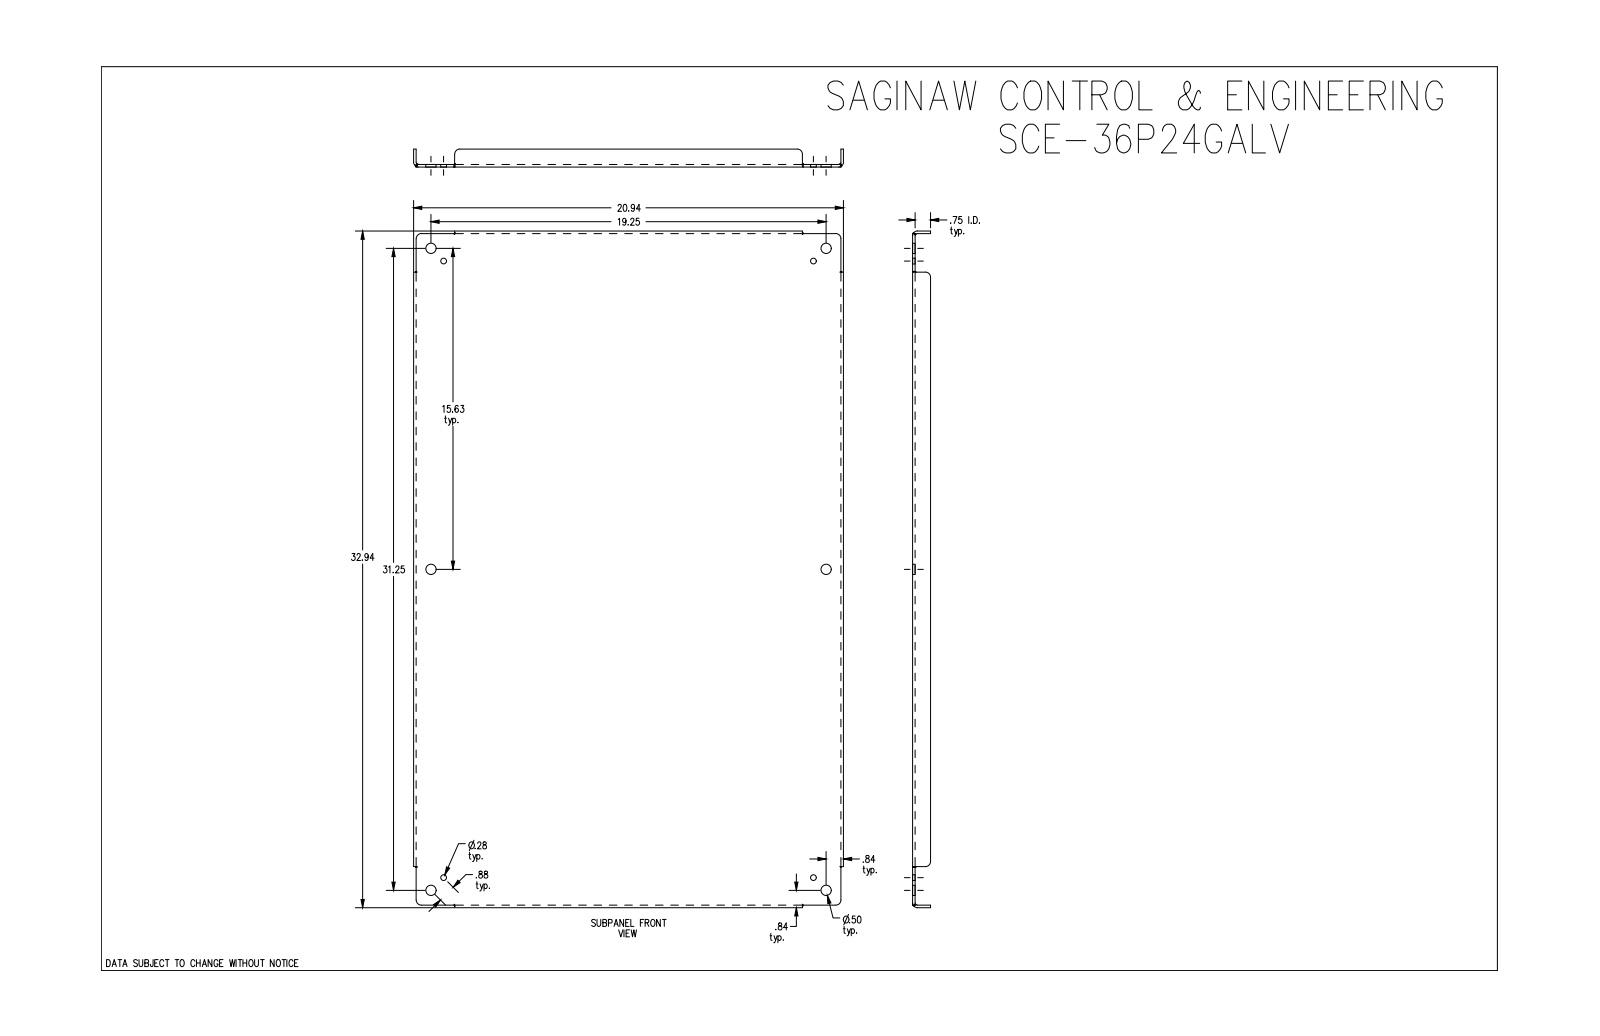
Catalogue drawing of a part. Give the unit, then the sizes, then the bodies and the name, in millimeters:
Units: millimetres
Overall size (bounding box): 836.6 × 531.8 × 22.2
Round holes (diameter × count): ⌀12.7 ×6, ⌀7.1 ×4
Partial cylindrical surfaces — rounded edges, fillets, slot ends (radius × count): R6.4 ×8, R2.8 ×4, R6 ×4
Main face-to-face distances: 3.2, 3.2, 528.7, 833.5, 525.4, 531.8, 19.1, 22.2, 830.2, 836.6
Hole centre spacings: 22.2, 381.5, 396.9, 473.5, 607.6, 629.7, 778.2, 910.7
Volume: 1 532 000 mm³ · Surface area: 975 500 mm²
Bodies: 1 solid, 84 faces (30 planar, 30 cylindrical, 24 other)
Part name (STEP PRODUCT): SCE-36P24GALV
STEP written by: SolidWorks 2019 (CONFIG_CONTROL_DESIGN)
